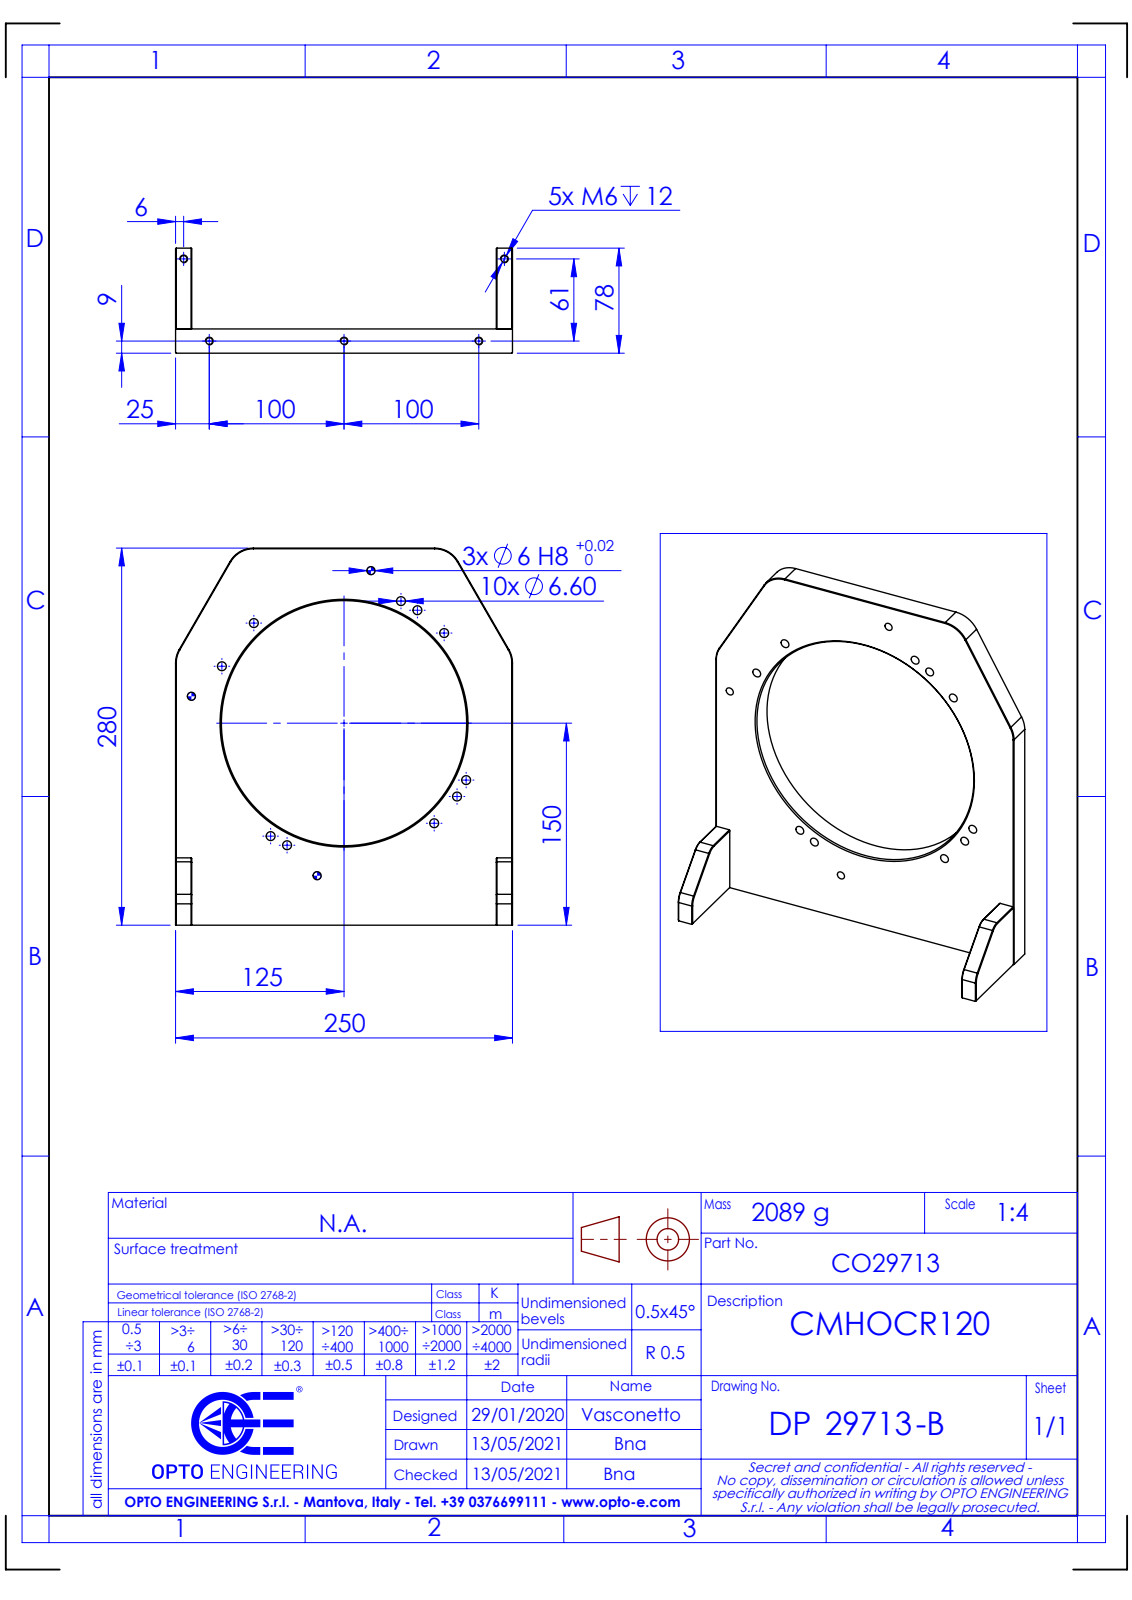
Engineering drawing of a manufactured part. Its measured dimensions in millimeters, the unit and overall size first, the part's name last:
Units: millimetres
Overall size (bounding box): 280 × 250 × 78
Round holes (diameter × count): ⌀11 ×14, ⌀6.6 ×10, ⌀5 ×5, ⌀6 ×3, ⌀182 ×1
Round bosses / shafts (diameter × count): ⌀10 ×2
Partial cylindrical surfaces — rounded edges, fillets, slot ends (radius × count): R20 ×4, R10 ×2
Main face-to-face distances: 18, 250, 12, 238, 226, 280, 6.4, 11.6, 50, 230
Hole centre spacings: 100, 141.42, 200, 13.95, 31.76, 39.87, 99.99, 110.38
Bodies: 0 solids, 192 faces (86 planar, 78 cylindrical, 28 other)
Part name (STEP PRODUCT): DP29713-B_CMHOCR120
STEP written by: SolidWorks 2021 (CONFIG_CONTROL_DESIGN)
